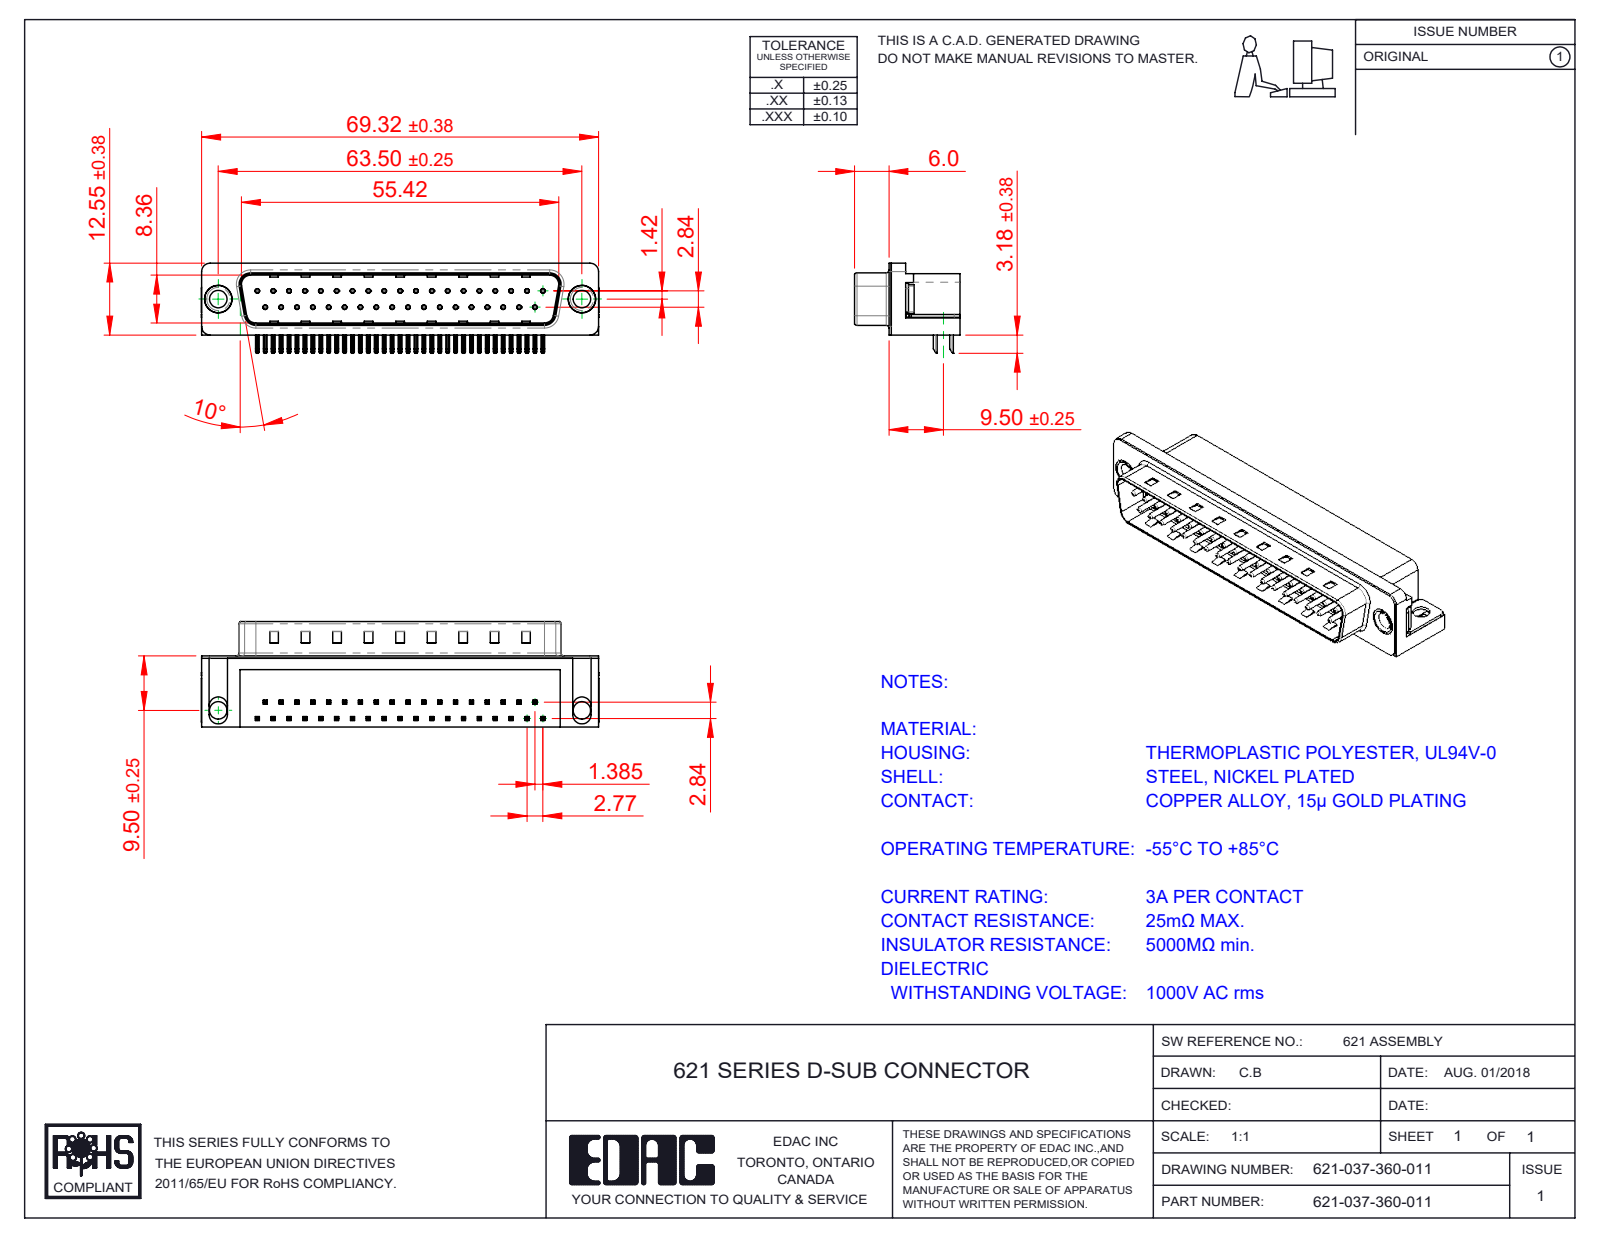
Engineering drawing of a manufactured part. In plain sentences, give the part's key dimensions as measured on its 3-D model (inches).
The part is named "621 Shell_37 Socket; 621-037-360-011; 621 Contact Bottom; 621 Housing_37 Socket (+3 more)". Its 3-D file was written by "SolidWorks 2016 (CONFIG_CONTROL_DESIGN)". It is 43 solids with 3157 faces: 2011 planar, 897 cylindrical and 249 other. Overall it measures 2.732 by 0.724 by 0.619 inches. Its volume is 0.525 cubic inches and its surface area 15.59 square inches. Round holes: 37 of diameter 0.014, 37 of diameter 0.031, 4 of diameter 0.12, 2 of diameter 0.157, 2 of diameter 0.189, 2 of diameter 0.197. Round bosses or shafts: 37 of diameter 0.03, 2 of diameter 0.193, 2 of diameter 0.187, 2 of diameter 0.152. Partial cylindrical surfaces (rounded edges, fillets, slot ends): 156 of radius 0.01, 74 of radius 0.005, 16 of radius 0.039, 9 of radius 0.02, 8 of radius 0.063, 7 of radius 0.059, 4 of radius 0.035, 4 of radius 0.079. The main face-to-face distances are 0.016, 0.472, 0.407, 0.345, 0.083, 0.067, 0.412, 0.428, 0.354, 0.488. The hole center spacings are 0.124, 0.109, 0.218, 0.327, 0.436, 0.545, 0.763, 0.872.
